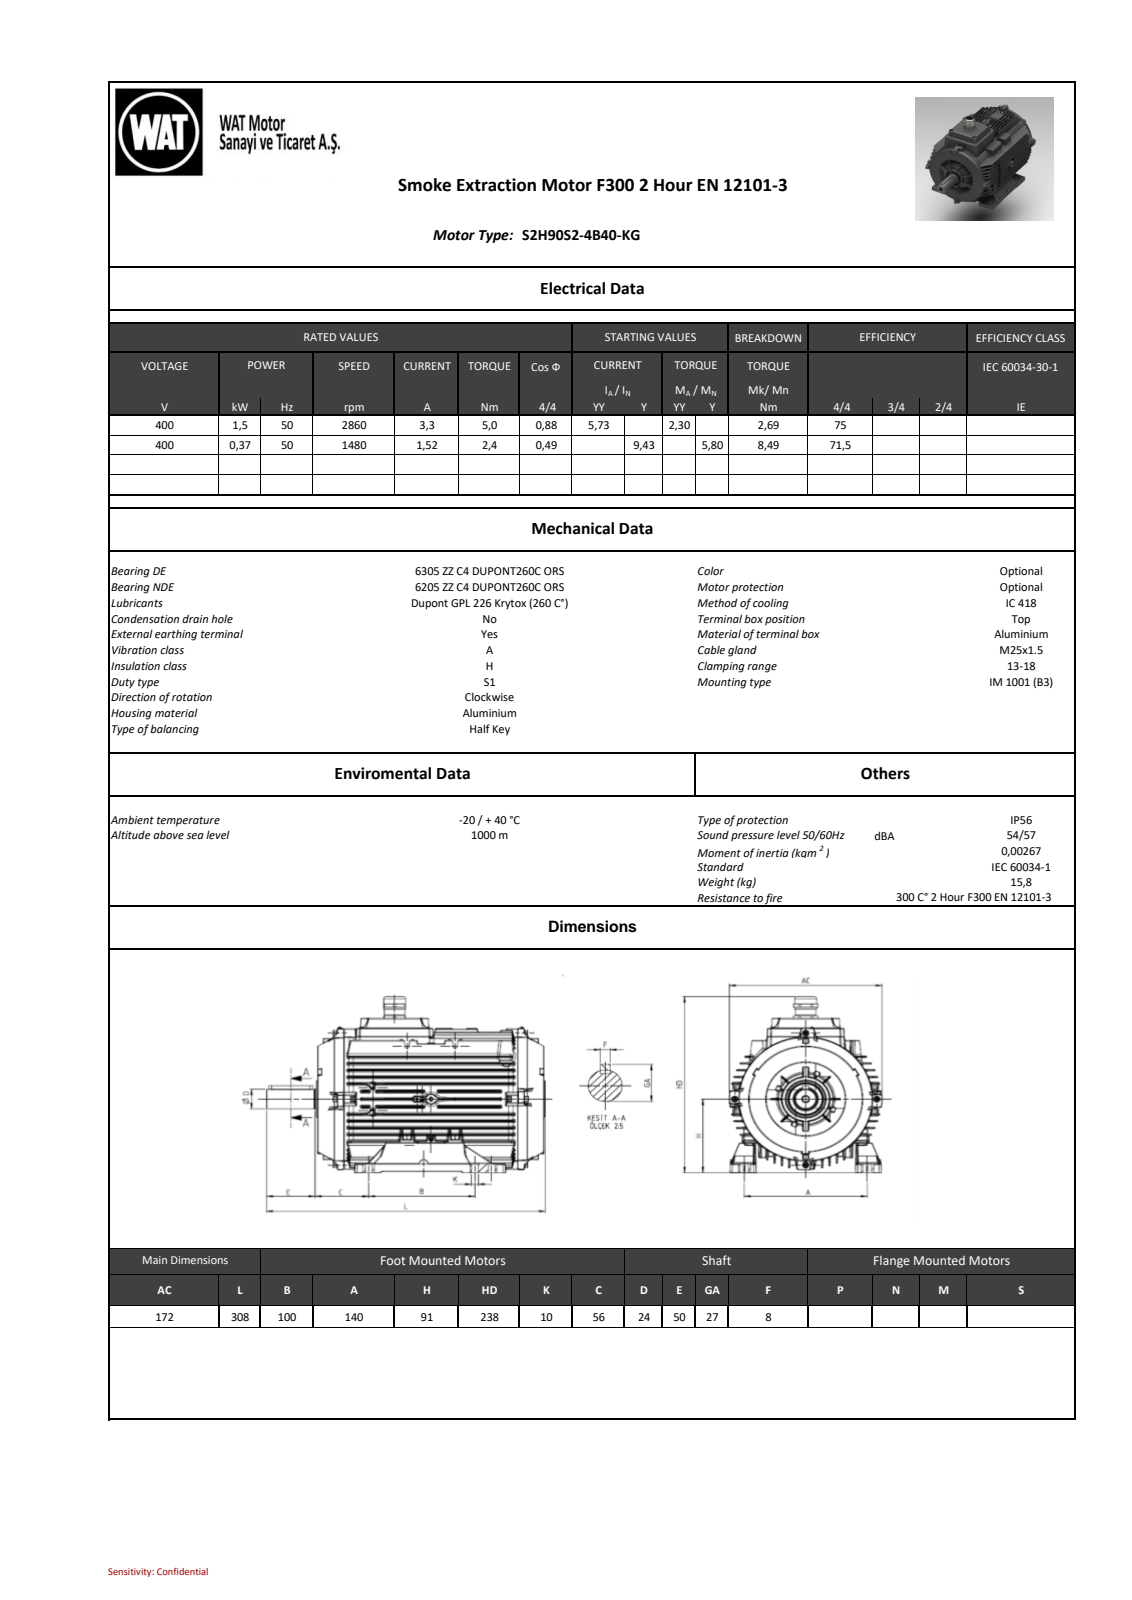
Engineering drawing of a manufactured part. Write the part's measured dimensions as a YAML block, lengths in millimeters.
part_name: "2603BE5CCA1Cd1yg"
step_written_by: "SIEMENS PLM Software NX 11.0 (AUTOMOTIVE_DESIGN)"
units: millimeters
bodies: {solids: 0, faces: 6677, planar: 1386, cylindrical: 2248, other: 3043}
overall_size: [307.75, 238, 172.47]
round_holes:
  - {diameter: 3.5, count: 4}
  - {diameter: 6.4, count: 1}
  - {diameter: 18, count: 1}
  - {diameter: 32, count: 1}
  - {diameter: 36.9, count: 1}
  - {diameter: 37.1, count: 1}
  - {diameter: 40, count: 1}
round_bosses_or_shafts:
  - {diameter: 9.2, count: 8}
  - {diameter: 8.5, count: 8}
  - {diameter: 8, count: 4}
  - {diameter: 5, count: 4}
  - {diameter: 29.59, count: 1}
  - {diameter: 28.14, count: 1}
  - {diameter: 26.62, count: 1}
  - {diameter: 25, count: 1}
partial_cylinders:
  - {radius: 1, count: 576}
  - {radius: 0.8, count: 569}
  - {radius: 0.5, count: 113}
  - {radius: 2, count: 64}
  - {radius: 0.98, count: 61}
  - {radius: 0.2, count: 59}
  - {radius: 8, count: 28}
  - {radius: 1.5, count: 18}
face_to_face_distances: [91.91, 7.5, 7.37, 23.57, 7.94, 82.85, 9.06, 16.43, 50.35, 74.81]
hole_center_spacings: [13, 147.54]
